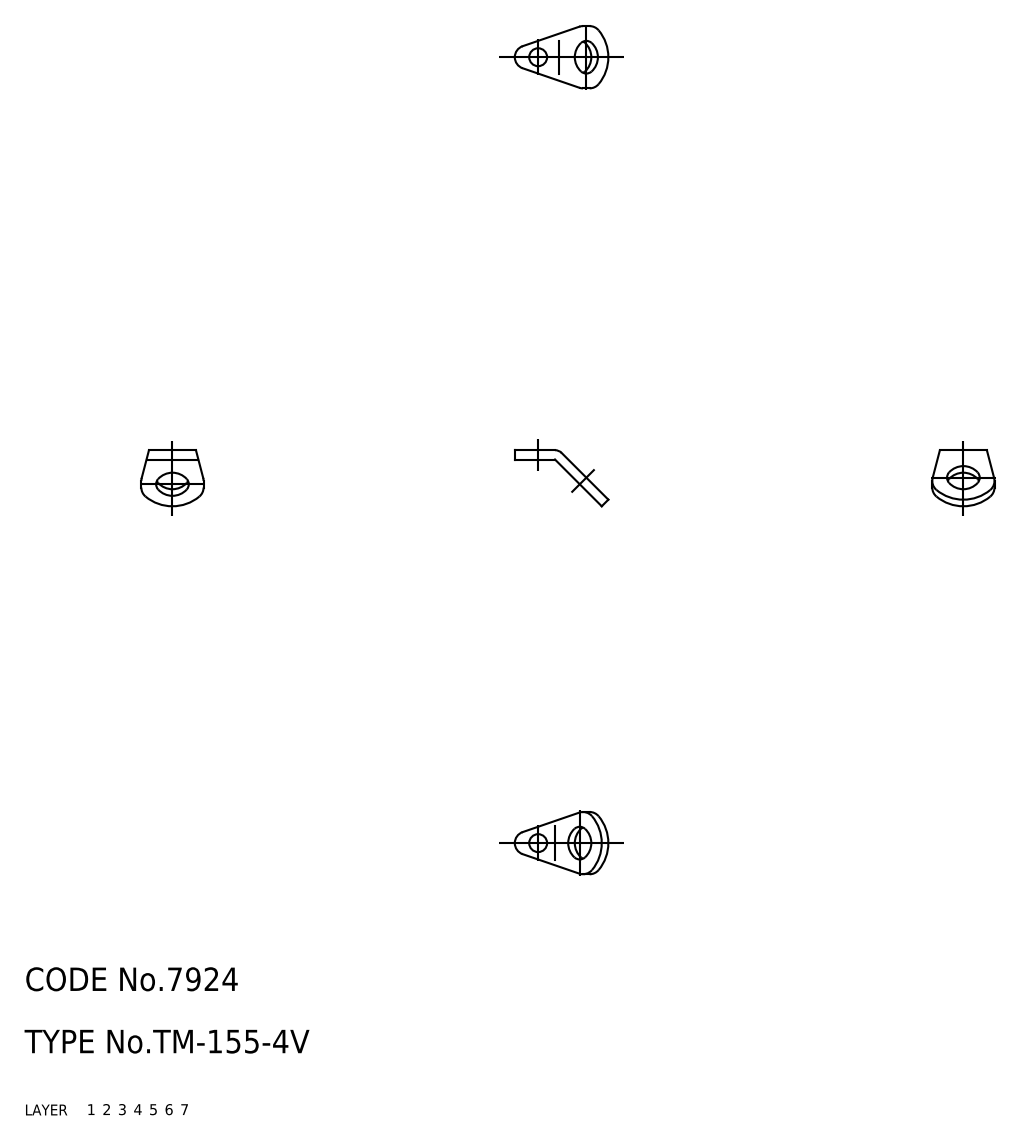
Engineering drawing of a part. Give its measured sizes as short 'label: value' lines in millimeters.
name: terminal
written by: CADfix (AUTOMOTIVE_DESIGN)
unit: mm
bodies: 1 solid, 21 faces (0 planar, 0 cylindrical, 21 other)
size: 12.02 × 8 × 7.21
volume: 73 mm³; area: 189 mm²
